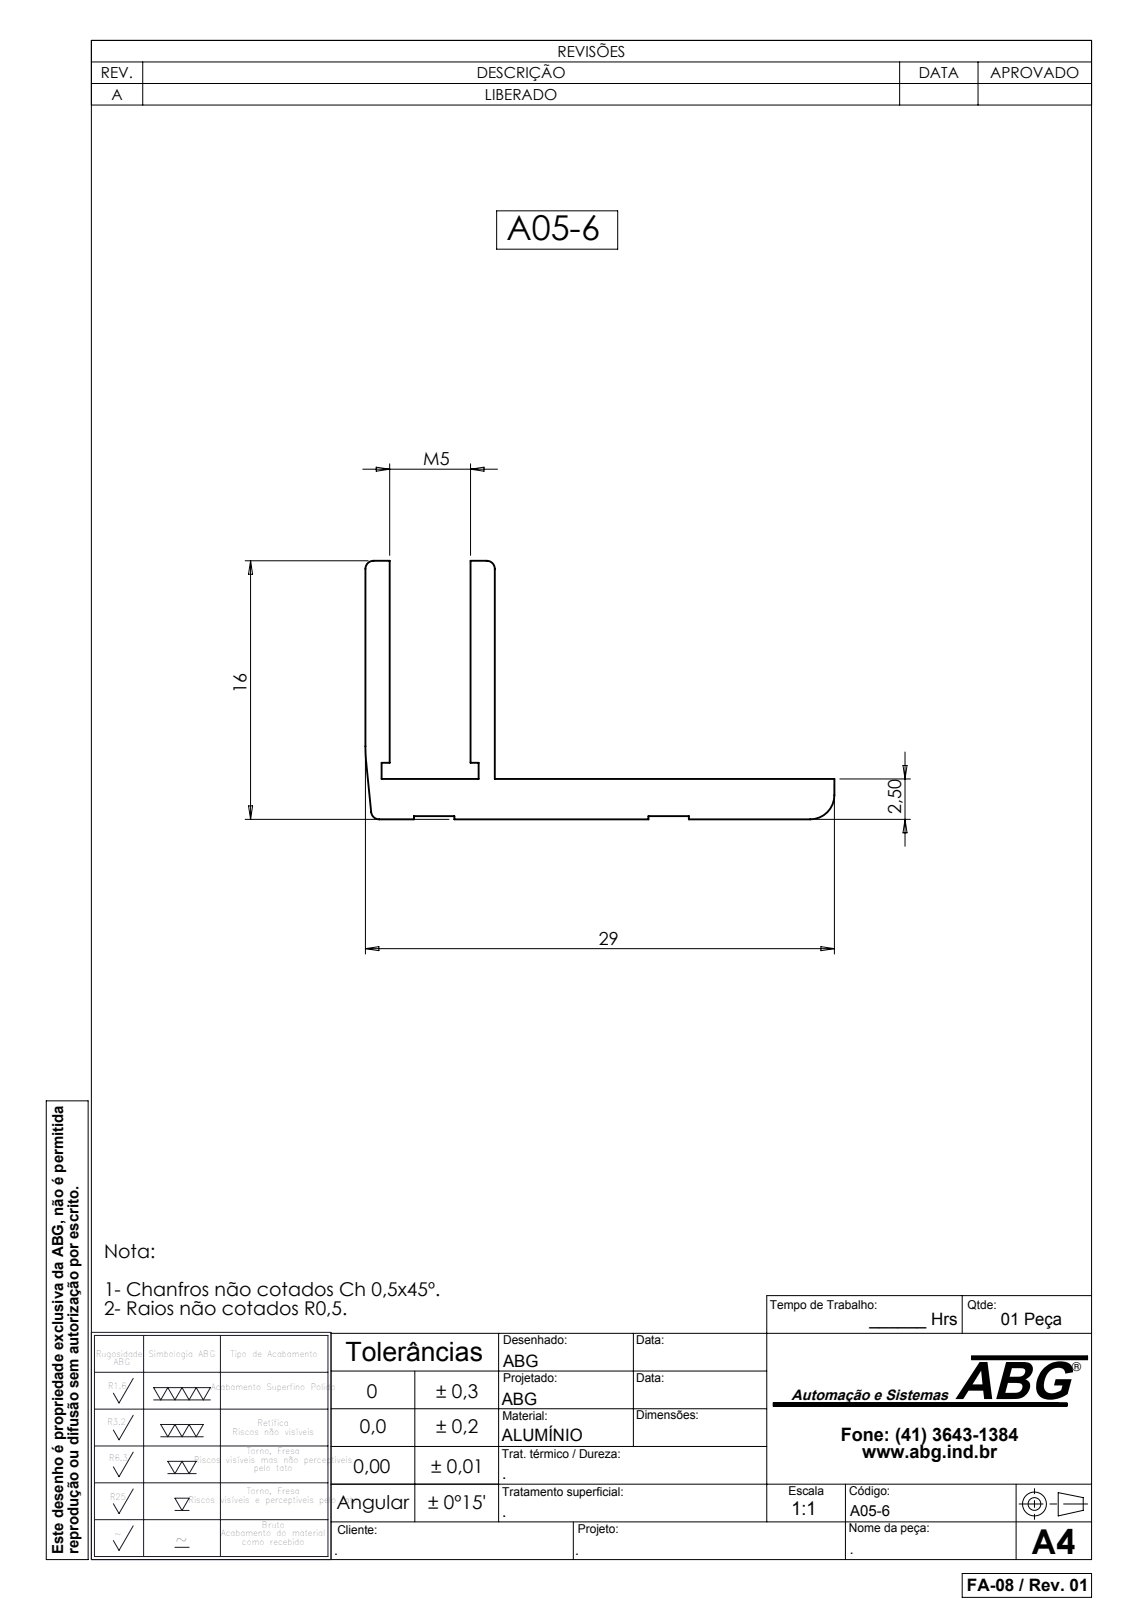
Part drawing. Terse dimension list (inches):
name: A05-6
written by: SolidWorks 2007 (CONFIG_CONTROL_DESIGN)
unit: in
bodies: 1 solid, 30 faces (25 planar, 5 cylindrical, 0 other)
size: 118.11 × 1.142 × 0.63
volume: 20.06 in³; area: 549.9 in²
rounds: 3× R0.02, 1× R0.059, 1× R0.413
face distances: 0.059, 0.256, 0.098, 0.197, 0.315, 0.091, 0.039, 0.63, 0.217, 0.531
